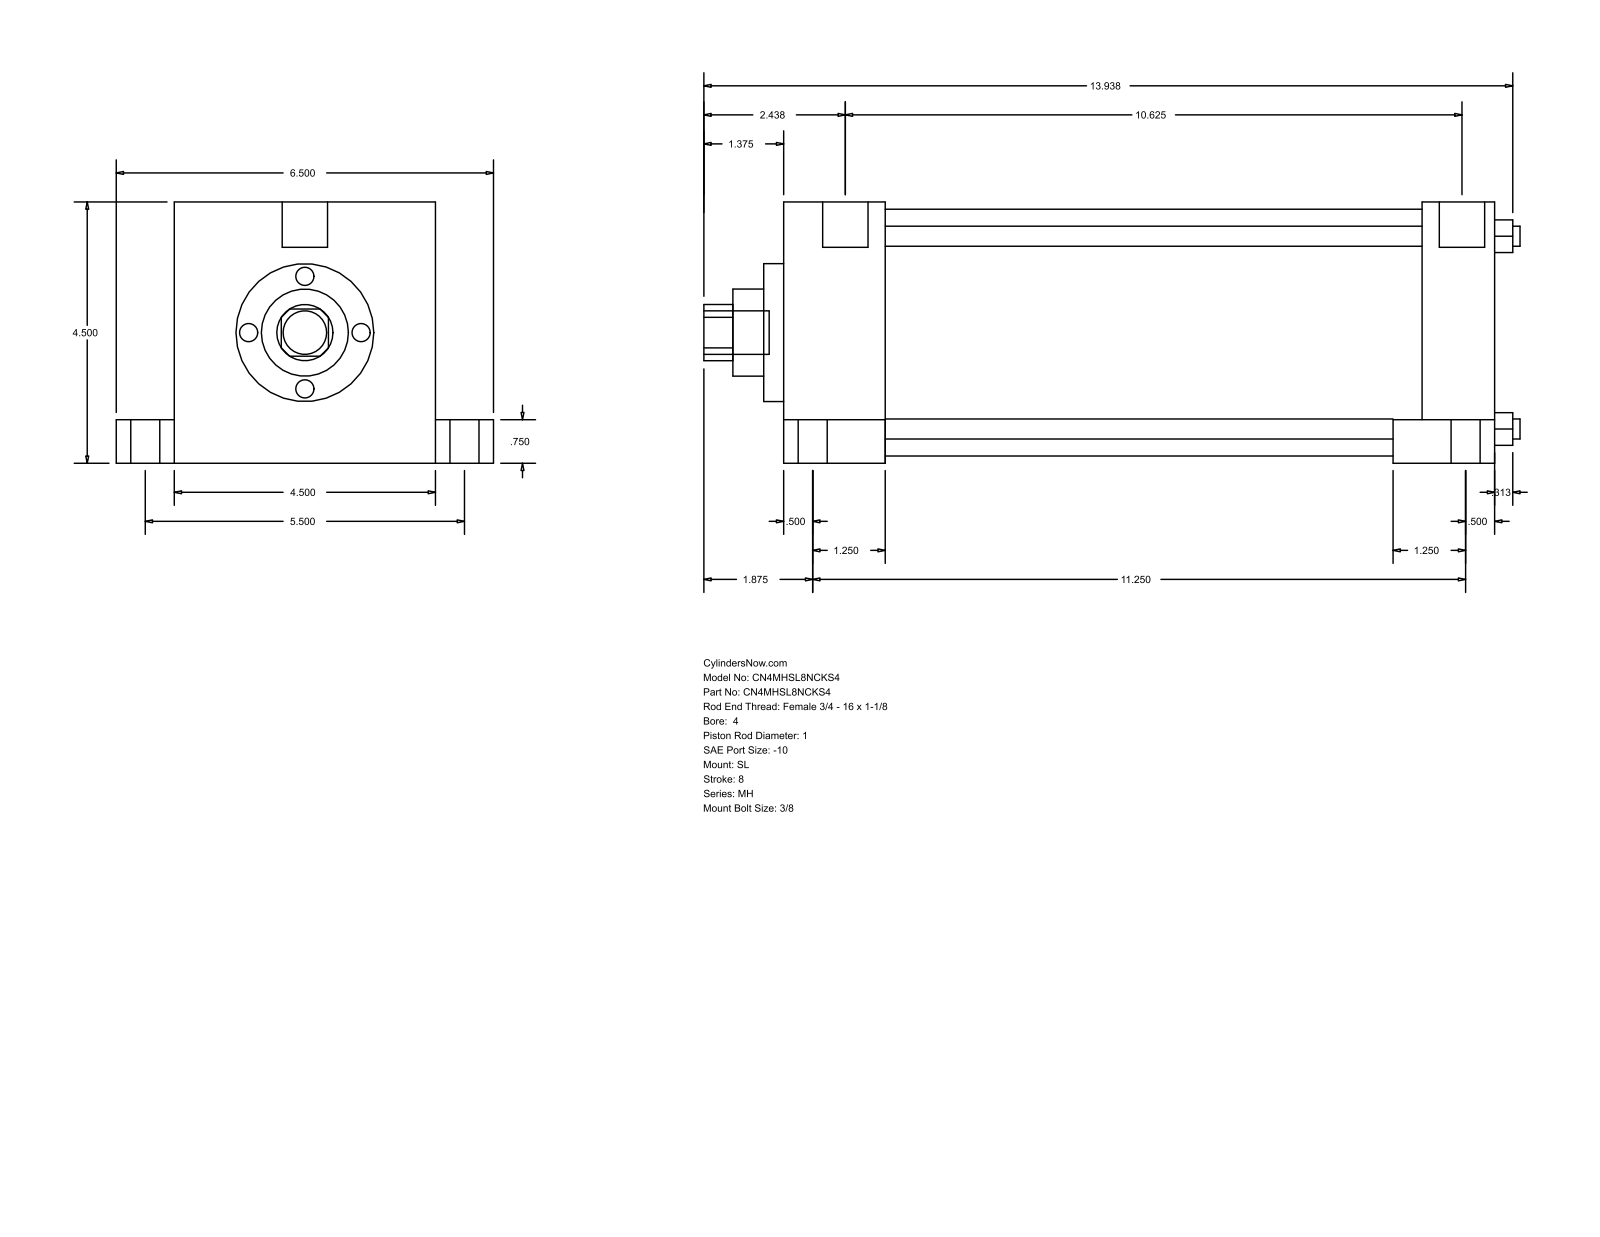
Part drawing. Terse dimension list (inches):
name: MH_SL__0400_1
written by: GSSL Pune (CONFIG_CONTROL_DESIGN)
unit: in
bodies: 0 solids, 110 faces (77 planar, 33 cylindrical, 0 other)
size: 14.063 × 6.5 × 4.5
holes: 4× ⌀0.345, 1× ⌀1, 1× ⌀1.5, 1× ⌀2.375, 1× ⌀4.25
bosses: 5× ⌀0.75, 4× ⌀0.5, 4× ⌀0.344, 2× ⌀0.781
rounds: 1× R0.484
face distances: 4.5, 12.25, 1.75, 10.5, 11, 9.25, 1.25, 1, 5.5, 0.75
hole spacings: 2.347, 3.32, 4.695
